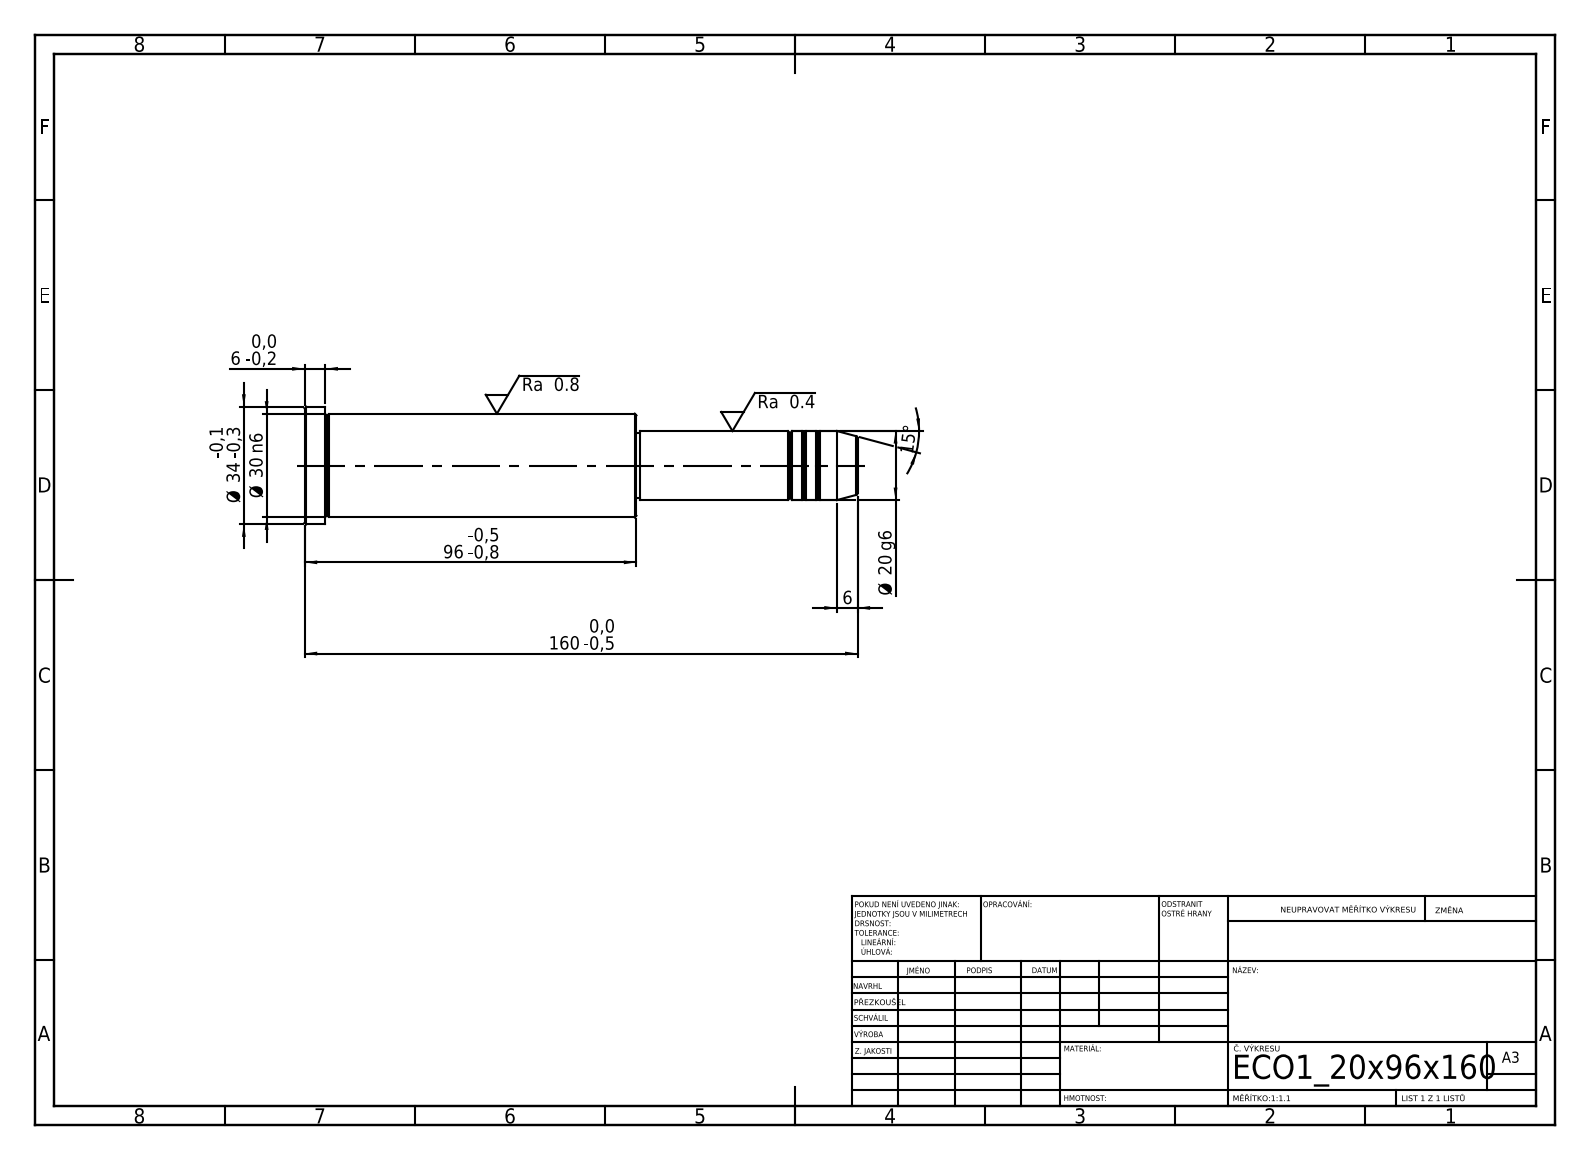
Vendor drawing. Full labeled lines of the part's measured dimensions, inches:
STEP written by: SolidWorks 2019 (CONFIG_CONTROL_DESIGN)
Units: inches
Bodies: 1 solid, 43 faces (5 planar, 14 cylindrical, 24 other)
Overall size (bounding box): 6.299 × 1.339 × 1.339
Volume: 5.414 in³ · Surface area: 23.24 in²
Round bosses / shafts (diameter × count): ⌀1.339 ×1, ⌀1.181 ×1, ⌀0.787 ×1, ⌀0.748 ×1
Main face-to-face distances: 3.78, 2.52, 6.299, 6.063, 3.543, 0.236, 2.48, 0.039, 3.583, 3.819
